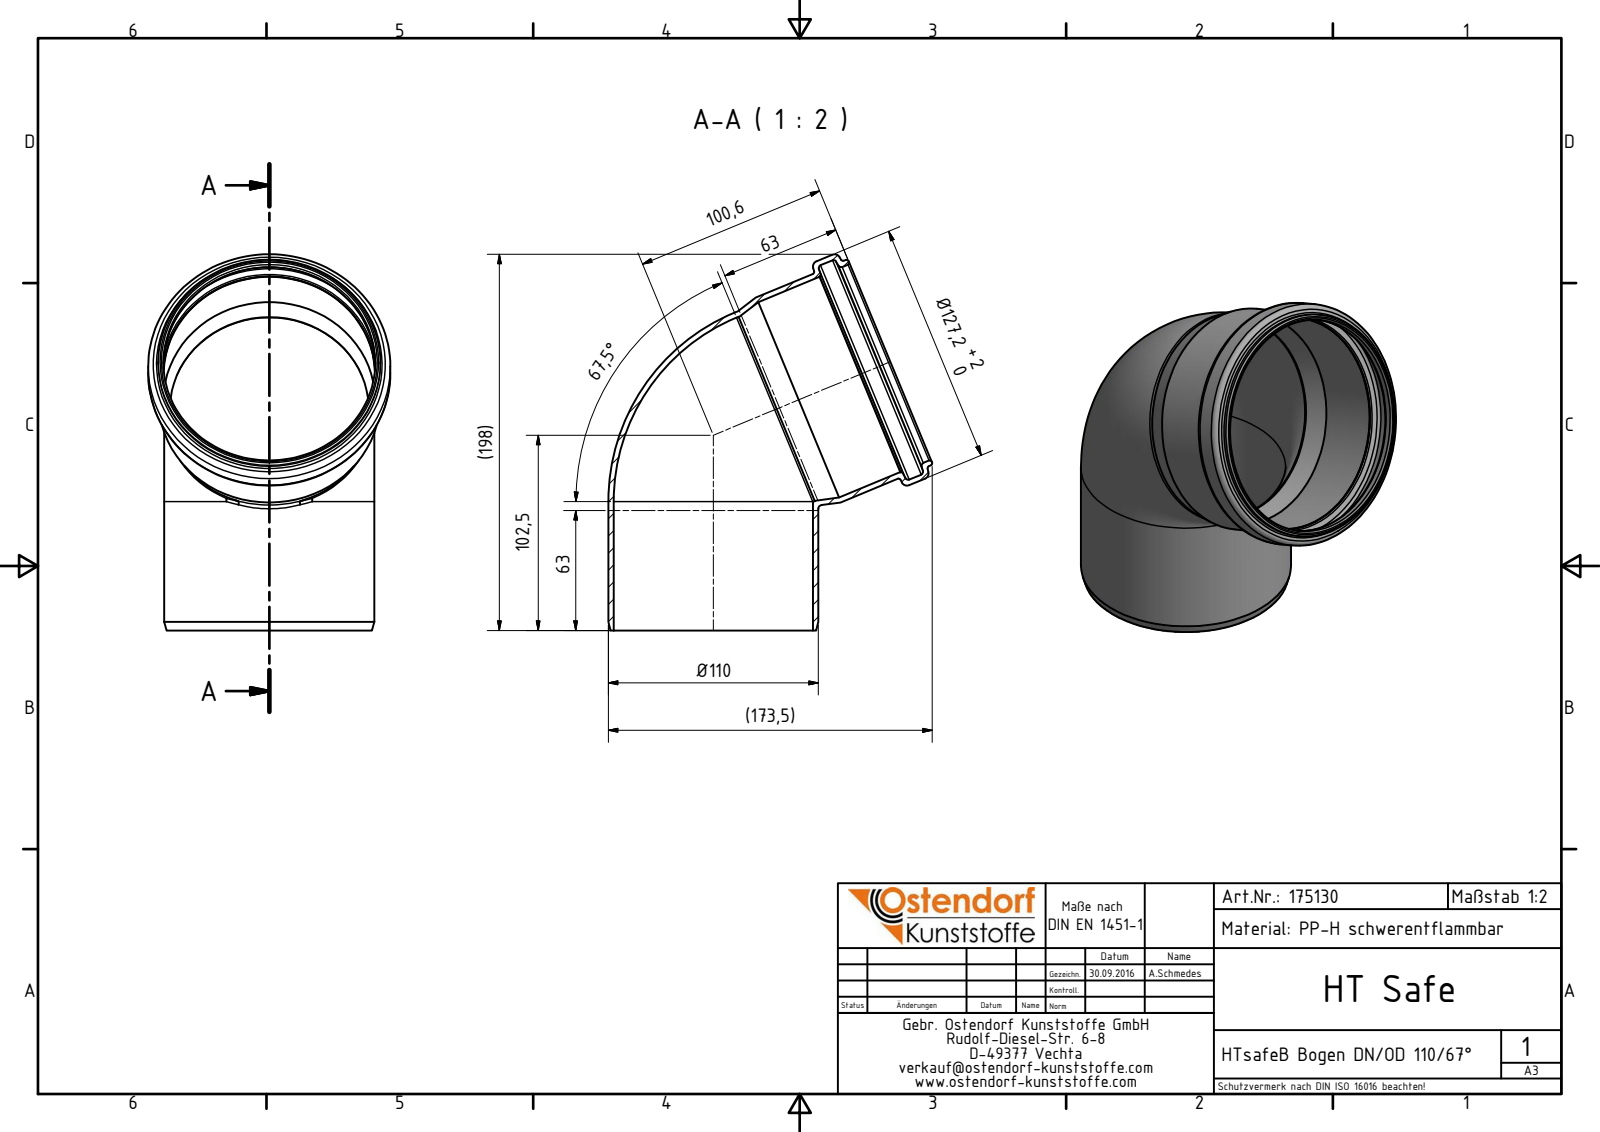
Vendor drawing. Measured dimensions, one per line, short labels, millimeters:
name: 175130 HTsafeB DN_OD 110_67°
written by: Autodesk Inventor 2016 (AUTOMOTIVE_DESIGN)
unit: mm
bodies: 1 solid, 37 faces (4 planar, 11 cylindrical, 22 other)
size: 197.46 × 170.12 × 127.2
volume: 178 156 mm³; area: 141 837 mm²
holes: 2× ⌀104.65, 2× ⌀111.3, 1× ⌀111, 1× ⌀121.8
bosses: 2× ⌀110.3, 1× ⌀127.2, 1× ⌀116.7, 1× ⌀116.4
face distances: 64.62, 47.28, 17.34
